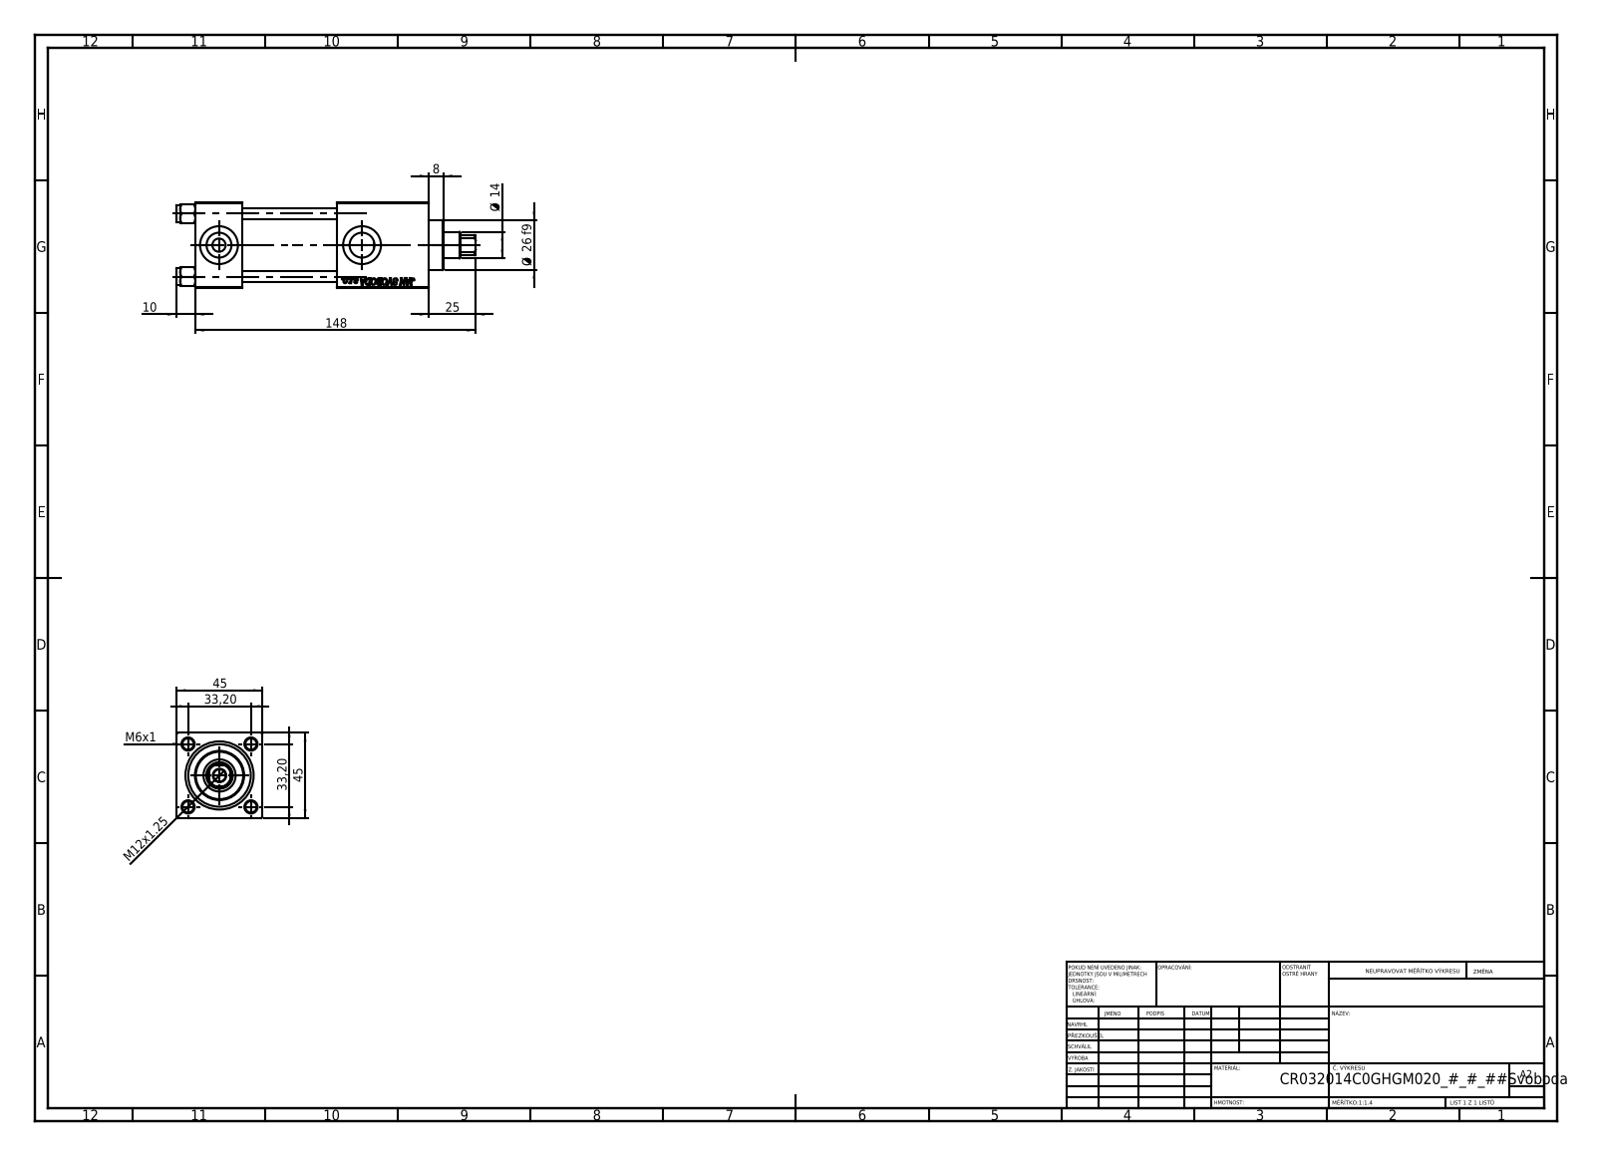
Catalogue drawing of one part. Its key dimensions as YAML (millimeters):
part_name: "V215_VC_A; V215CR_VCP_C; V215CR_C_TYCINKA; NUT_M5_C (+1 more)"
step_written_by: "SolidWorks 2019 (CONFIG_CONTROL_DESIGN)"
units: millimeters
bodies: {solids: 11, faces: 1147, planar: 525, cylindrical: 86, other: 536}
overall_size: [158, 45, 45]
volume: 193896
surface_area: 67085
round_holes:
  - {diameter: 6, count: 4}
  - {diameter: 7, count: 2}
  - {diameter: 13.16, count: 2}
  - {diameter: 20, count: 2}
  - {diameter: 6.5, count: 1}
  - {diameter: 14, count: 1}
  - {diameter: 17, count: 1}
  - {diameter: 24, count: 1}
  - {diameter: 32, count: 1}
  - {diameter: 33, count: 1}
round_bosses_or_shafts:
  - {diameter: 9, count: 4}
  - {diameter: 38, count: 1}
  - {diameter: 26, count: 1}
partial_cylinders:
  - {radius: 6.5, count: 1}
face_to_face_distances: [45, 25, 98, 123, 50, 75, 48, 94.3, 69.3, 19.3]
hole_center_spacings: [23.48, 33.2, 46.95, 75.5]
